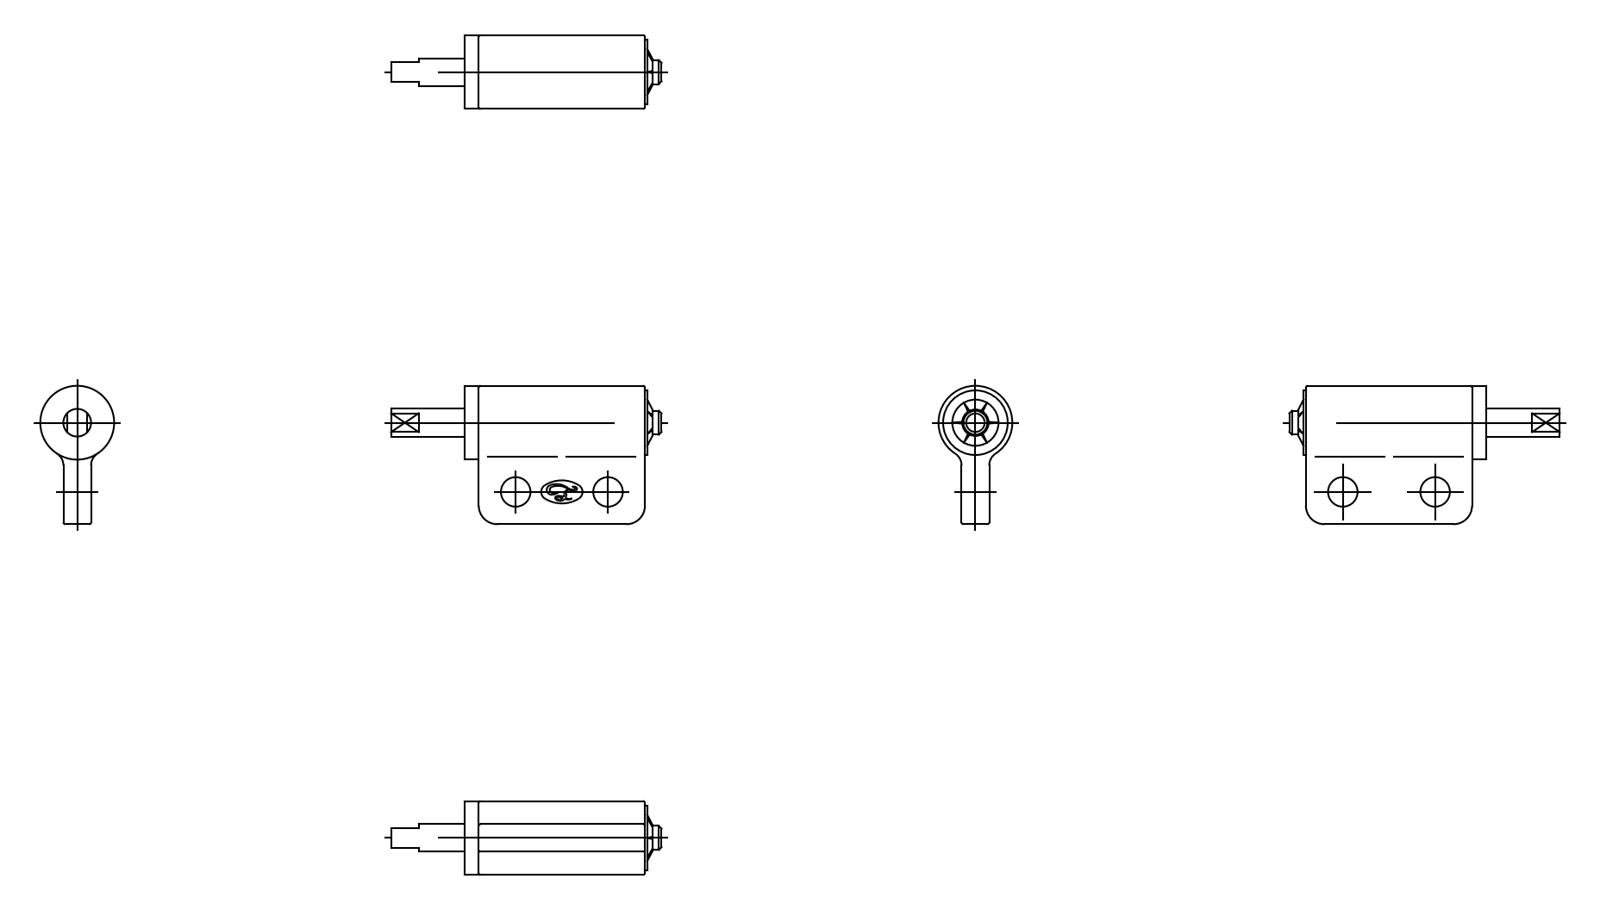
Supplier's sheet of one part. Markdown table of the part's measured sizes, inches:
| quantity | value |
| --- | --- |
| STEP written by | spGate 18.9.1 (****-****-****-****) (AUTOMOTIVE_DESIGN) |
| units | inches |
| bodies | 1 solid, 147 faces (38 planar, 77 cylindrical, 32 other) |
| overall size | 1.154 × 0.591 × 0.315 |
| volume | 0.082 in³ |
| surface area | 2.15 in² |
| round holes (diameter × count) | 0.126 × 2, 0.118 × 1, 0.236 × 1 |
| round bosses / shafts (diameter × count) | 0.315 × 1, 0.276 × 1, 0.224 × 1, 0.118 × 1, 0.102 × 1 |
| partial cylindrical surfaces (radius × count) | 0.039 × 9, 0.008 × 6, 0.011 × 2, 0.022 × 2, 0.031 × 2, 0.033 × 2, 0.033 × 2, 0.059 × 2 |
| main face-to-face distances | 0.118, 0.049, 0.167, 0.217, 0.768, 0.709, 0.059, 0.719, 0.778, 0.061 |
| hole center spacings | 0.198, 0.394 |
